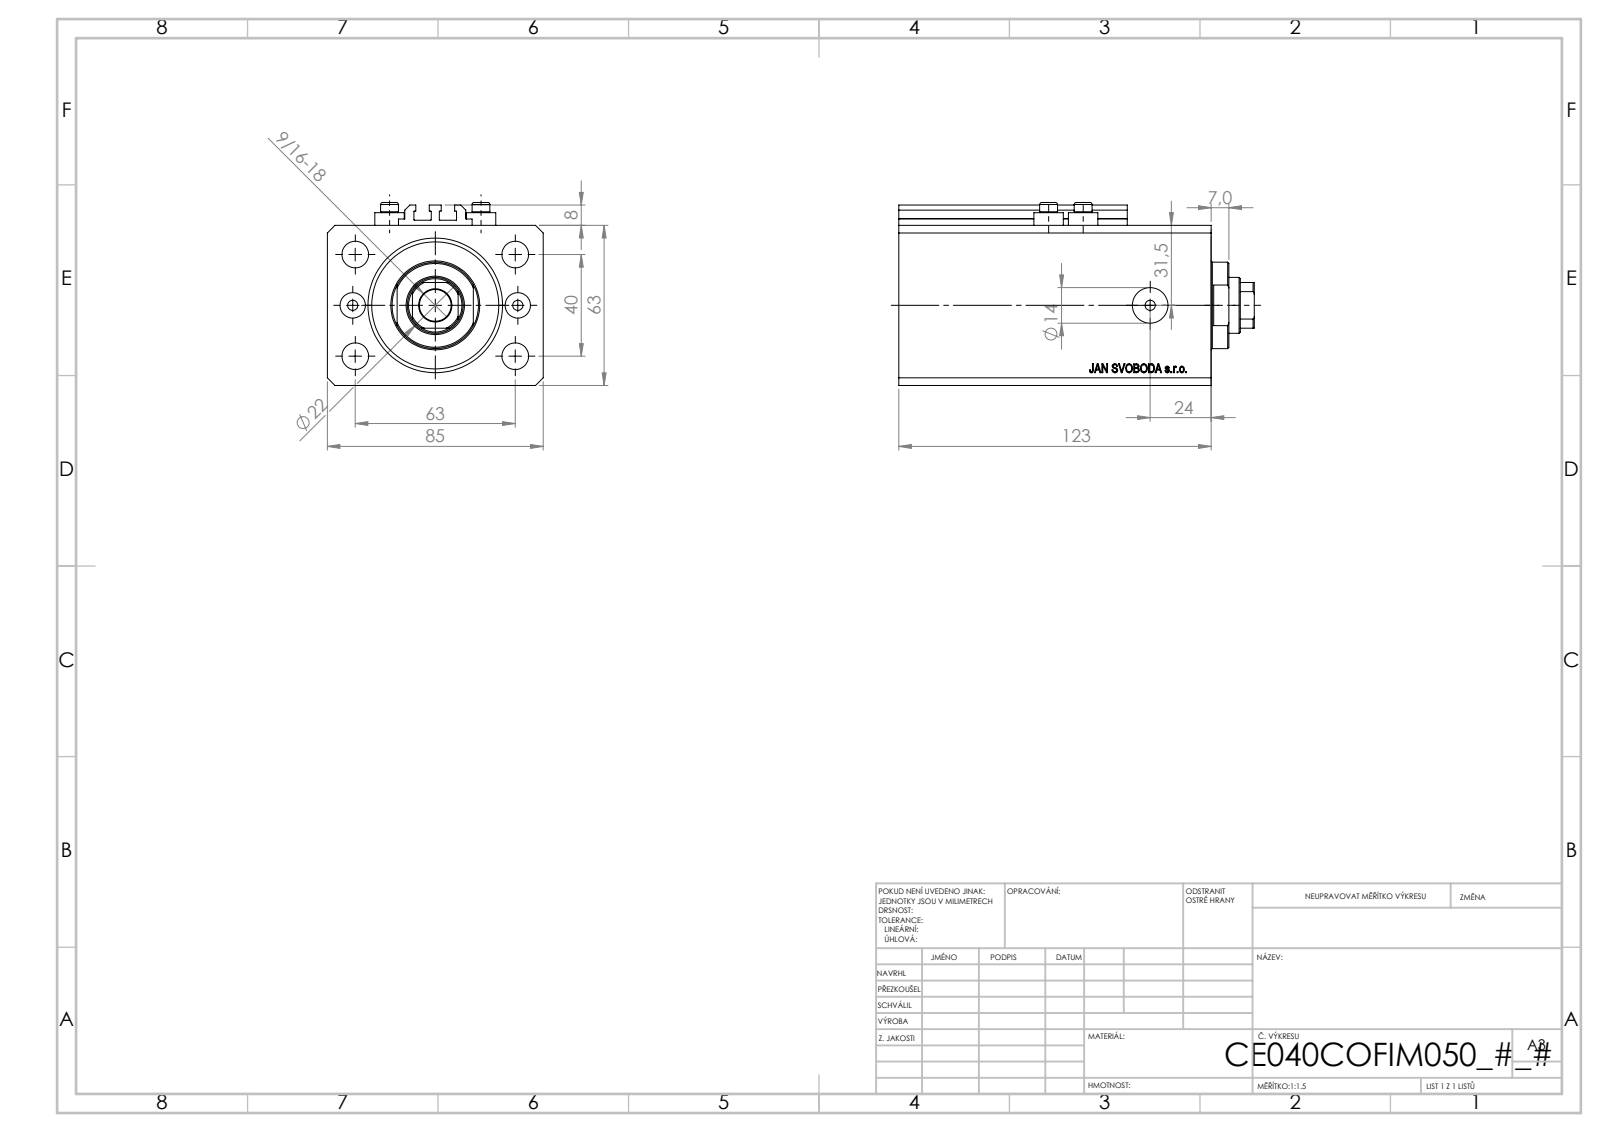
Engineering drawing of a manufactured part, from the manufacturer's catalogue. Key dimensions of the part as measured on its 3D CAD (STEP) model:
Part name (STEP PRODUCT): ALLEN BOLT V250CE; V250CE_C_VCP; V250CE_VC_C; V250CE_C_Body
STEP written by: SolidWorks 2019 (CONFIG_CONTROL_DESIGN)
Units: millimetres
Bodies: 8 solids, 1034 faces (504 planar, 86 cylindrical, 444 other)
Overall size (bounding box): 140 × 85 × 72
Volume: 587 344 mm³ · Surface area: 113 688 mm²
Round holes (diameter × count): ⌀4 ×8, ⌀10.5 ×4, ⌀10 ×2, ⌀14 ×2, ⌀12.5 ×1, ⌀22 ×1, ⌀40 ×1, ⌀53 ×1
Round bosses / shafts (diameter × count): ⌀11.6 ×4, ⌀7 ×4, ⌀34 ×1
Partial cylindrical surfaces — rounded edges, fillets, slot ends (radius × count): R0.2 ×10, R10.5 ×1
Main face-to-face distances: 63, 85, 123, 17, 106, 11.4, 94.6, 111.6, 2.5, 10
Hole centre spacings: 20.02, 37.31, 67.05, 13.6, 32.5, 36, 38.48, 40
